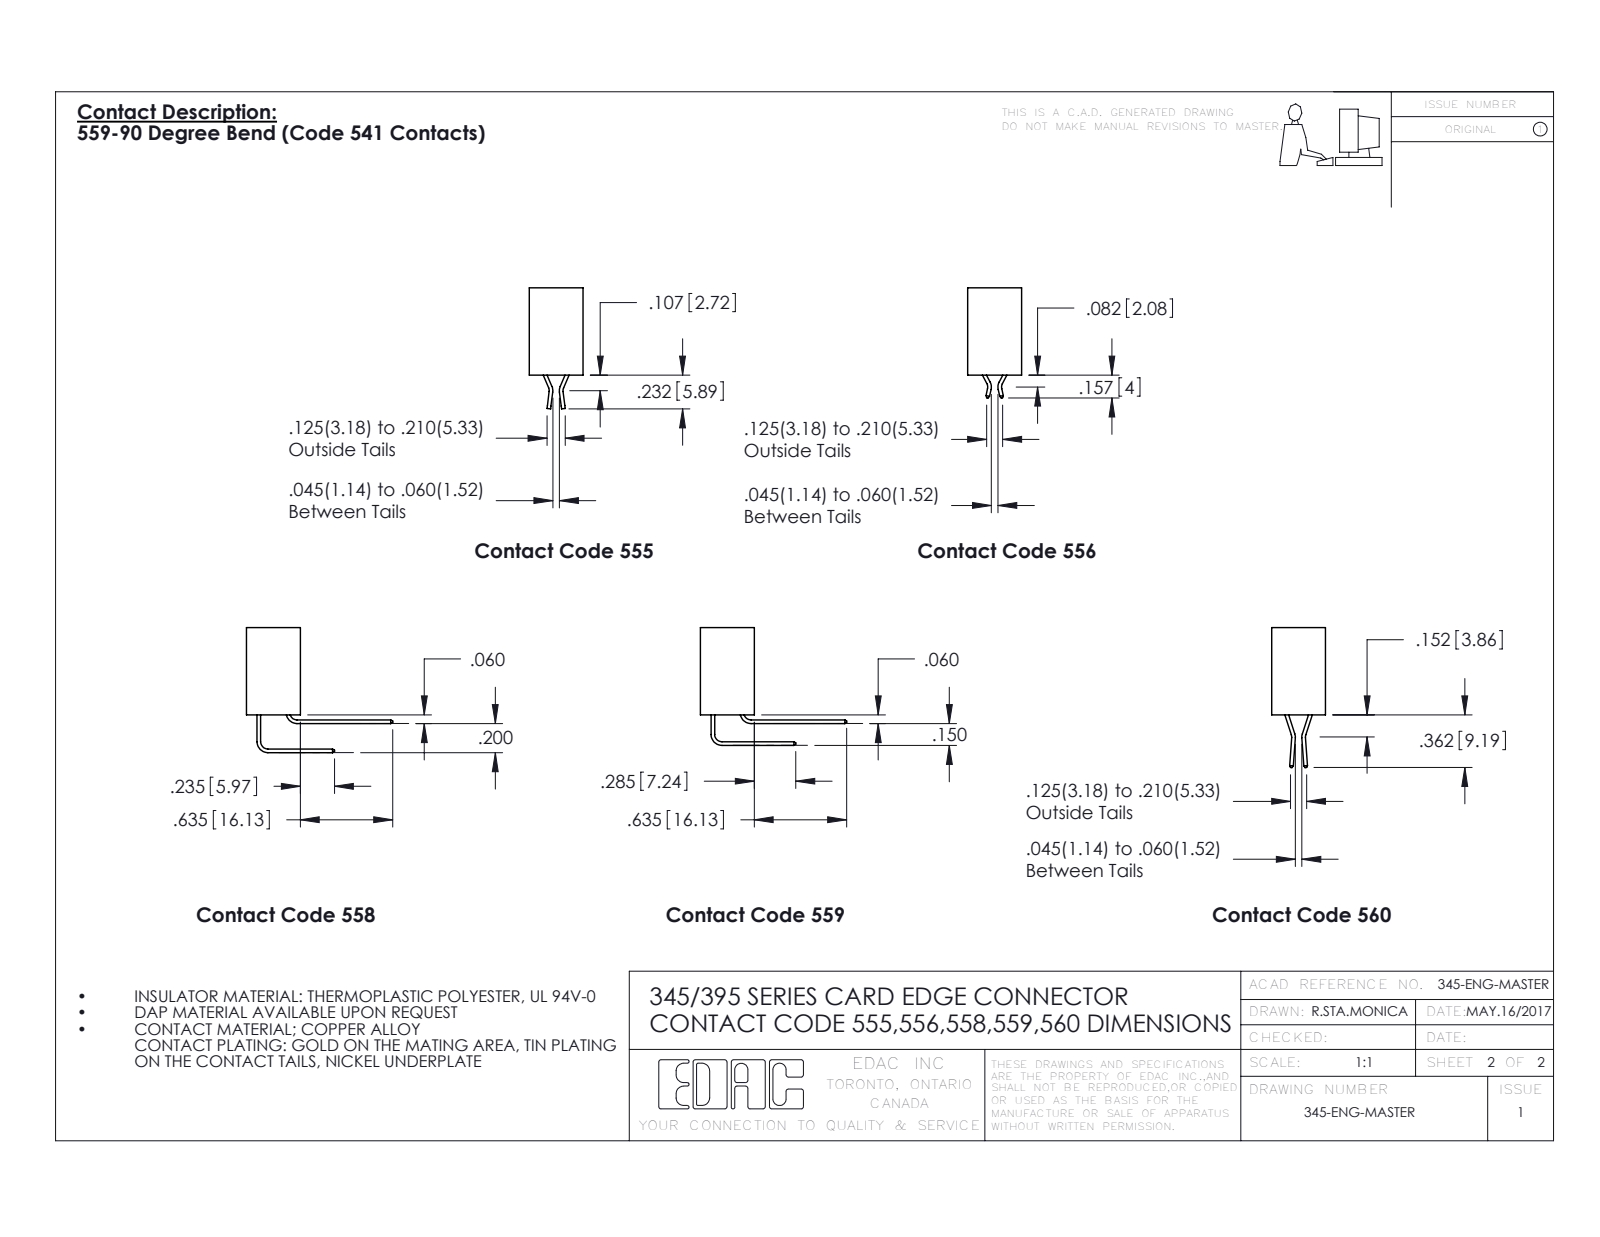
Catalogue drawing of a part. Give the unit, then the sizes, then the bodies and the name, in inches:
Units: inches
Overall size (bounding box): 2.535 × 0.859 × 0.605
Round holes (diameter × count): ⌀0.128 ×2, ⌀0.064 ×1
Partial cylindrical surfaces — rounded edges, fillets, slot ends (radius × count): R0.006 ×34, R0.01 ×22, R0.007 ×6, R0.031 ×6, R0.026 ×3, R0.031 ×2, R0.04 ×2, R0.014 ×1
Main face-to-face distances: 0.072, 0.298, 0.2, 0.37, 0.098, 0.272, 0.025, 0.225, 0.1, 0.149
Hole centre spacings: 2.275
Volume: 0.354 in³ · Surface area: 11.86 in²
Bodies: 18 solids, 1150 faces (798 planar, 352 cylindrical, 0 other)
Part name (STEP PRODUCT): 395-017-558-412; 345 Part_0.110 Offset - Side Mount; 345-292-001_558 Tail - 2
STEP written by: SolidWorks 2016 (CONFIG_CONTROL_DESIGN)
